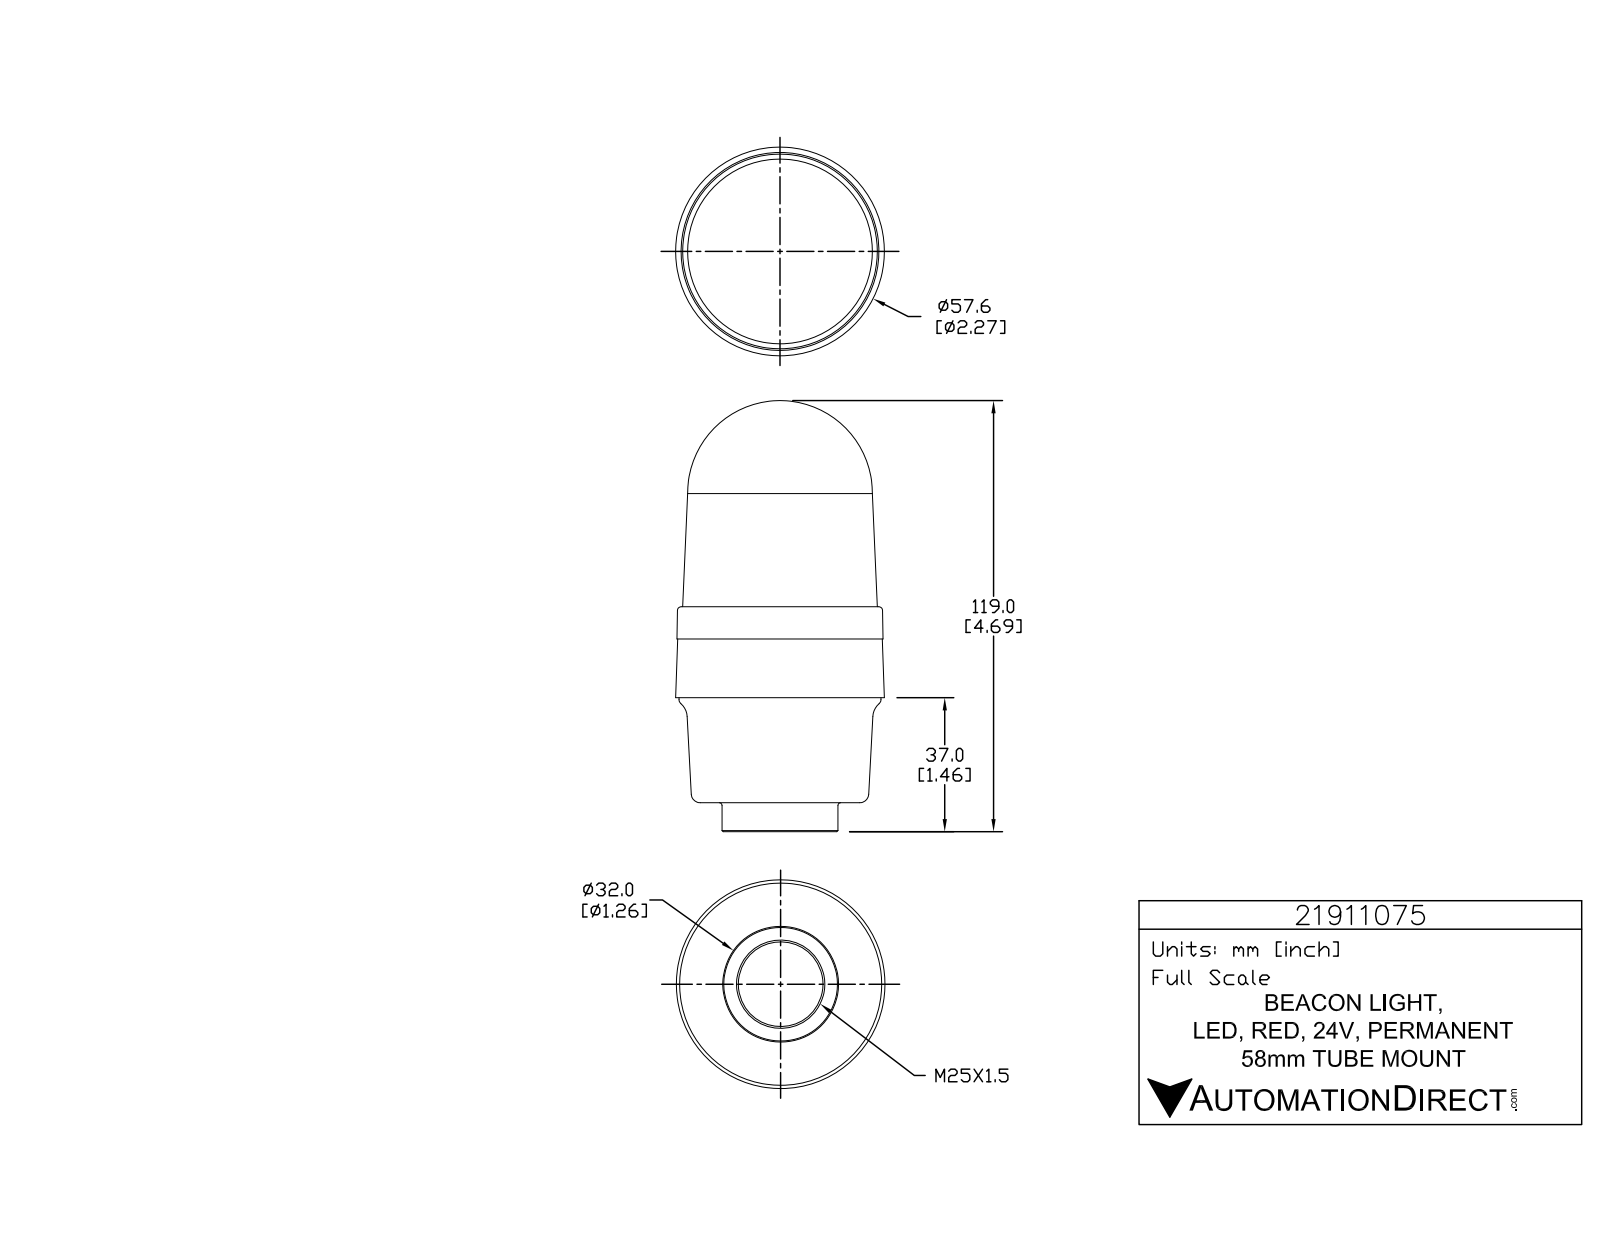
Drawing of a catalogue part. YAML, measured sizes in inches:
part_name: "21911075"
step_written_by: "SolidWorks 2015 (AUTOMOTIVE_DESIGN)"
units: inches
bodies: {solids: 1, faces: 791, planar: 525, cylindrical: 168, other: 98}
overall_size: [4.685, 2.269, 2.269]
volume: 13.89
surface_area: 34.06
round_holes:
  - {diameter: 0.039, count: 3}
  - {diameter: 0.92, count: 1}
round_bosses_or_shafts:
  - {diameter: 0.226, count: 3}
  - {diameter: 0.056, count: 3}
  - {diameter: 2.197, count: 1}
  - {diameter: 1.26, count: 1}
partial_cylinders:
  - {radius: 0.008, count: 6}
  - {radius: 0.008, count: 6}
  - {radius: 0.008, count: 6}
  - {radius: 0.131, count: 6}
  - {radius: 0.004, count: 3}
  - {radius: 0.005, count: 3}
  - {radius: 0.008, count: 3}
  - {radius: 0.008, count: 3}
face_to_face_distances: [0.315, 1.142, 1.457, 0.988, 2.13, 2.445, 0.35, 0.638, 1.78, 2.094]
